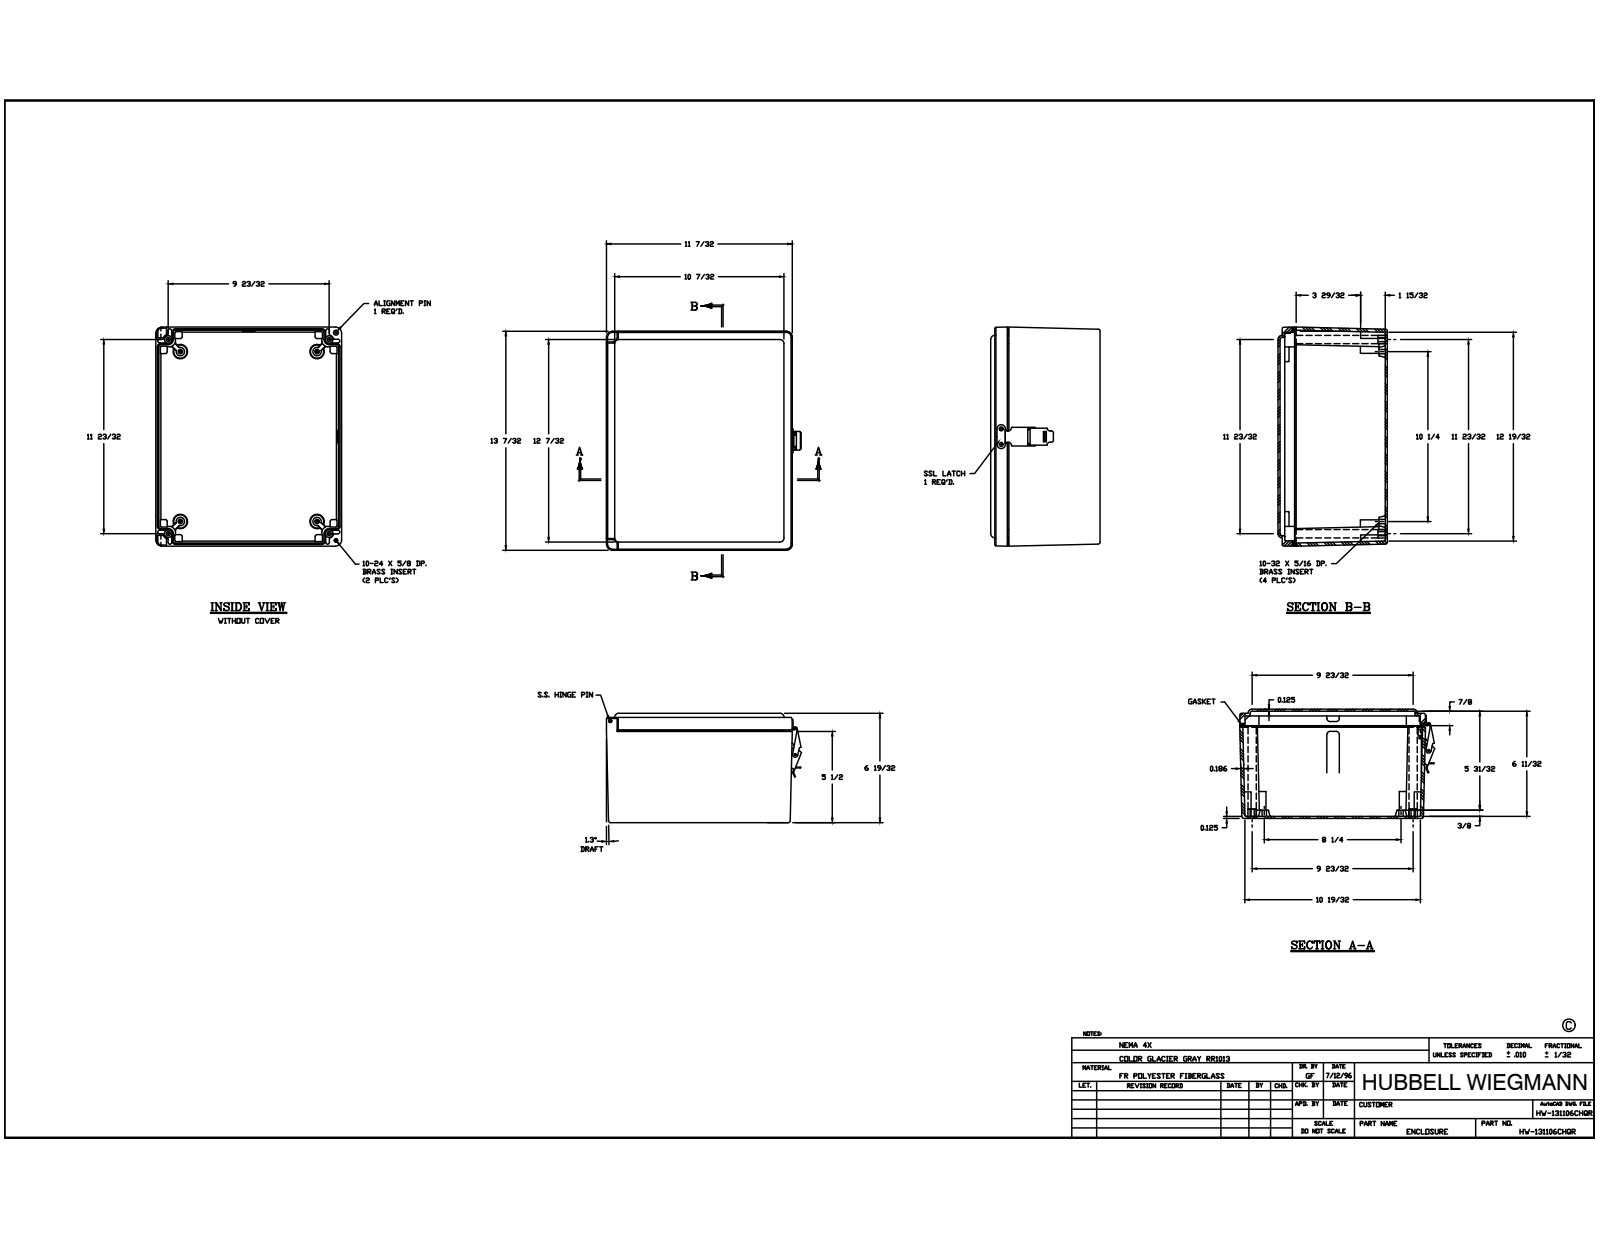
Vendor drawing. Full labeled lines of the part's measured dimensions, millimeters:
Part name (STEP PRODUCT): WP1311HPLBOX; 0.3125-18 X 0.563 DP BRASS INSERT; 10-32 X0.3125 DP BRASS INSERT; 10-24 X 0.625 DP BRASS INSERT (+8 more)
STEP written by: Autodesk Inventor 2014 (AUTOMOTIVE_DESIGN)
Units: millimetres
Bodies: 30 solids, 1115 faces (436 planar, 379 cylindrical, 300 other)
Overall size (bounding box): 335.76 × 300.65 × 167.48
Volume: 1 797 000 mm³ · Surface area: 846 958 mm²
Round holes (diameter × count): ⌀7.14 ×6, ⌀2.64 ×4, ⌀3.56 ×4, ⌀3.96 ×4, ⌀3.97 ×4, ⌀7.94 ×4, ⌀13.49 ×4, ⌀2.44 ×2, ⌀3.3 ×2, ⌀3.43 ×2, ⌀3.68 ×2, ⌀4.76 ×2
Round bosses / shafts (diameter × count): ⌀9.52 ×2, ⌀5.94 ×2, ⌀3.56 ×2, ⌀2.42 ×2, ⌀9.42 ×1, ⌀7.62 ×1, ⌀7.6 ×1, ⌀4.7 ×1
Partial cylindrical surfaces — rounded edges, fillets, slot ends (radius × count): R0.79 ×60, R3.17 ×38, R1.59 ×29, R6.35 ×10, R1.14 ×8, R1.5 ×8, R4.78 ×8, R9.53 ×8
Main face-to-face distances: 3.17, 164.31, 4.72, 167.48, 161.14, 3.18, 161.13, 157.96, 6.35, 19.05
Hole centre spacings: 290.76, 308.13, 318.28, 14.59, 26.38, 40.97, 228.95, 240.26
